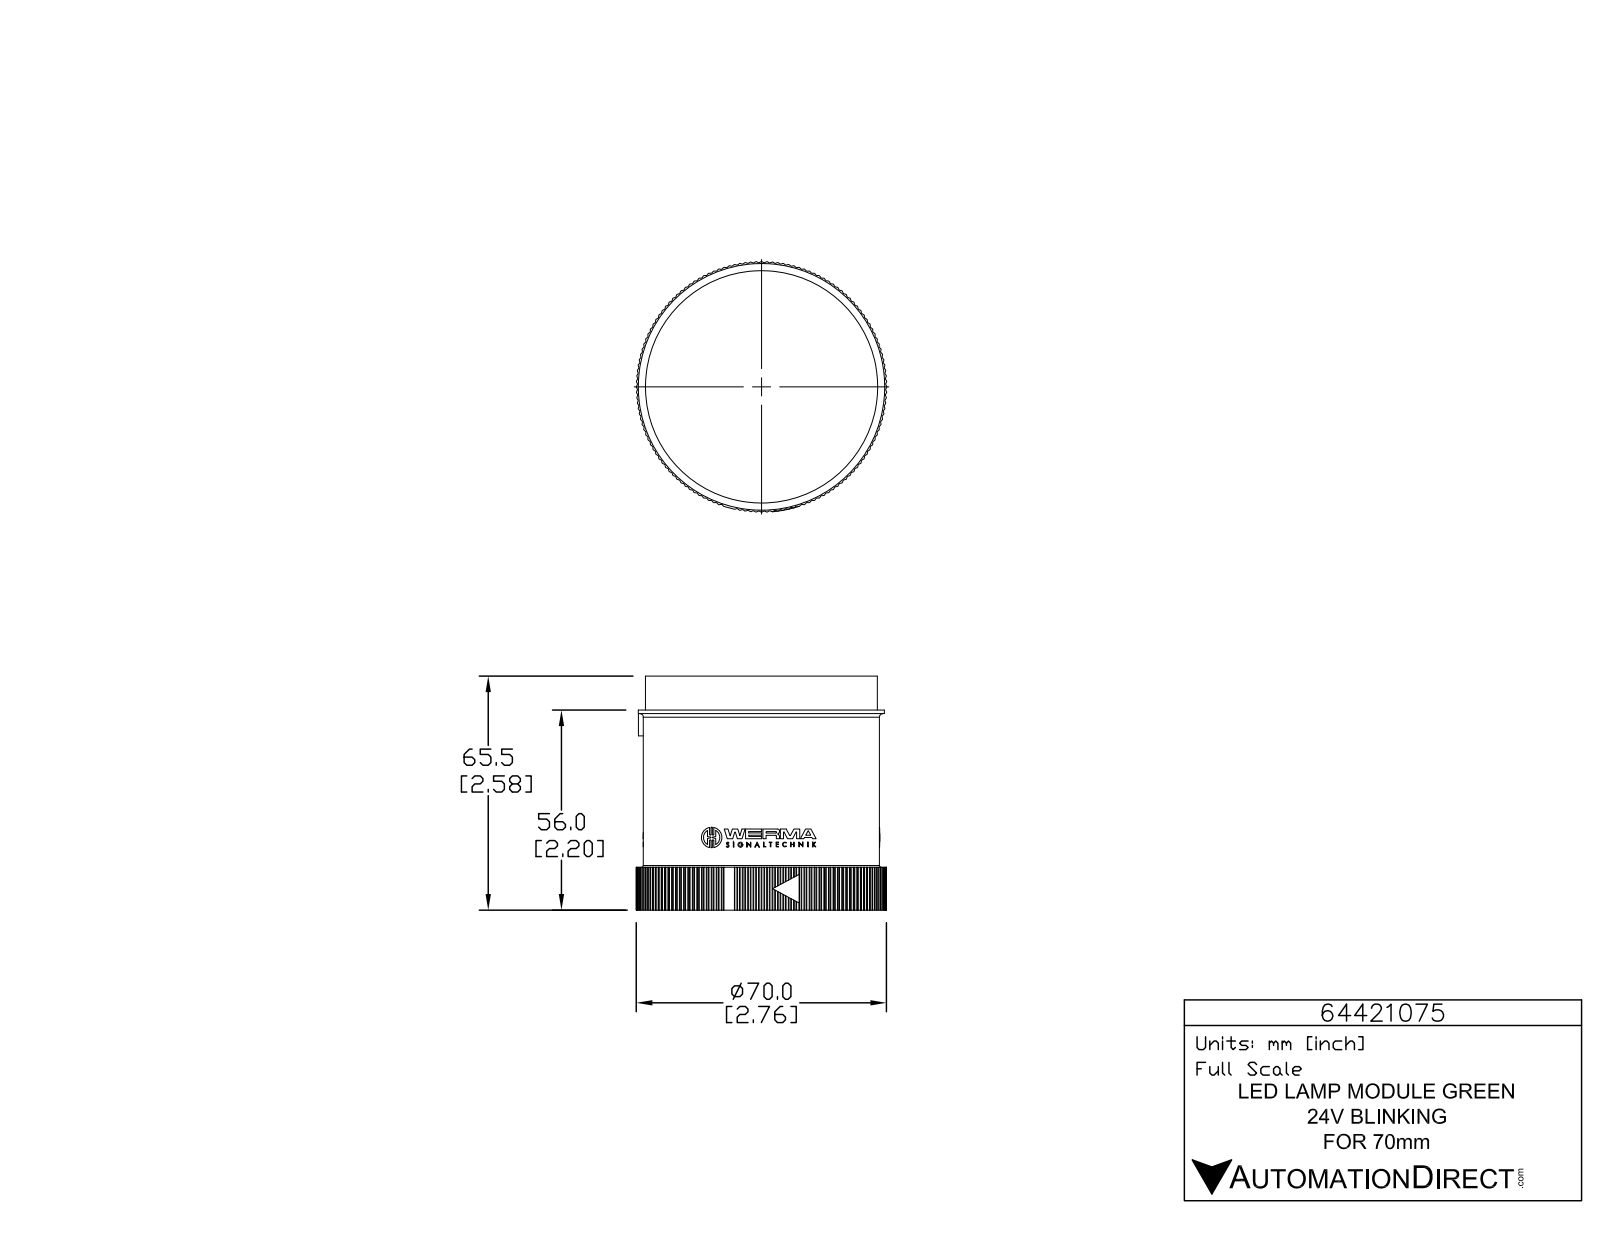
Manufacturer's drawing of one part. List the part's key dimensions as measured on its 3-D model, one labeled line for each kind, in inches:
Part name (STEP PRODUCT): 64421075
STEP written by: SolidWorks 2015 (AUTOMOTIVE_DESIGN)
Units: inches
Bodies: 1 solid, 1400 faces (832 planar, 563 cylindrical, 5 other)
Overall size (bounding box): 2.762 × 2.762 × 2.579
Volume: 12.02 in³ · Surface area: 37.48 in²
Round holes (diameter × count): ⌀0.039 ×3, ⌀2.575 ×1
Round bosses / shafts (diameter × count): ⌀0.226 ×3, ⌀0.056 ×3, ⌀2.717 ×1, ⌀2.606 ×1, ⌀2.559 ×1
Partial cylindrical surfaces — rounded edges, fillets, slot ends (radius × count): R0.008 ×285, R0.008 ×6, R0.008 ×6, R0.008 ×6, R0.131 ×6, R0.004 ×3, R0.005 ×3, R0.008 ×3
Main face-to-face distances: 2.201, 2.451, 0.378, 2.579, 2.205, 1.827, 0.374, 2.452, 0.472, 0.094
